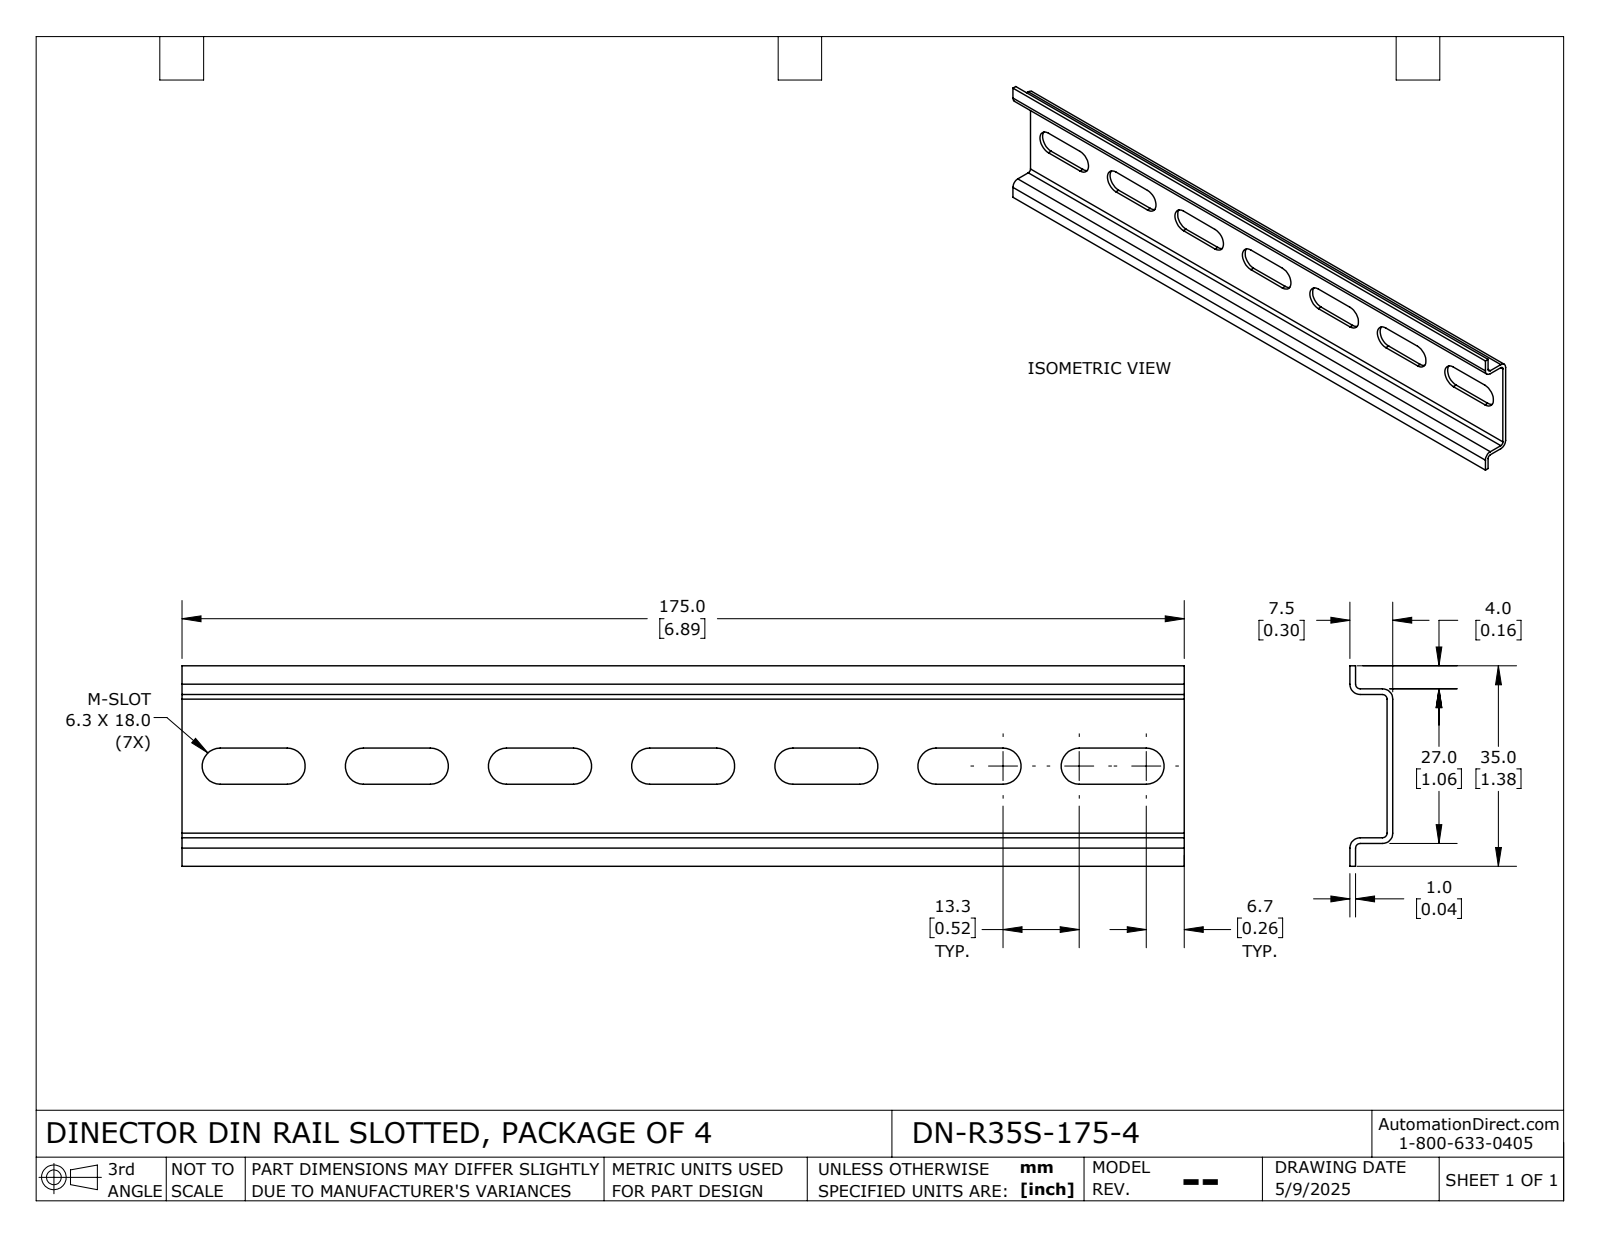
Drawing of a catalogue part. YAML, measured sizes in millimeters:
part_name: "DN-R35S-175-4_Default"
step_written_by: "SolidWorks 2024 (CONFIG_CONTROL_DESIGN)"
units: millimeters
bodies: {solids: 1, faces: 50, planar: 28, cylindrical: 22, other: 0}
overall_size: [175, 35, 7.5]
volume: 7275
surface_area: 15294
partial_cylinders:
  - {radius: 3.15, count: 14}
  - {radius: 0.8, count: 4}
  - {radius: 1.8, count: 4}
face_to_face_distances: [1, 6.5, 26, 7.5, 5.5, 27, 25, 4, 5, 30]
